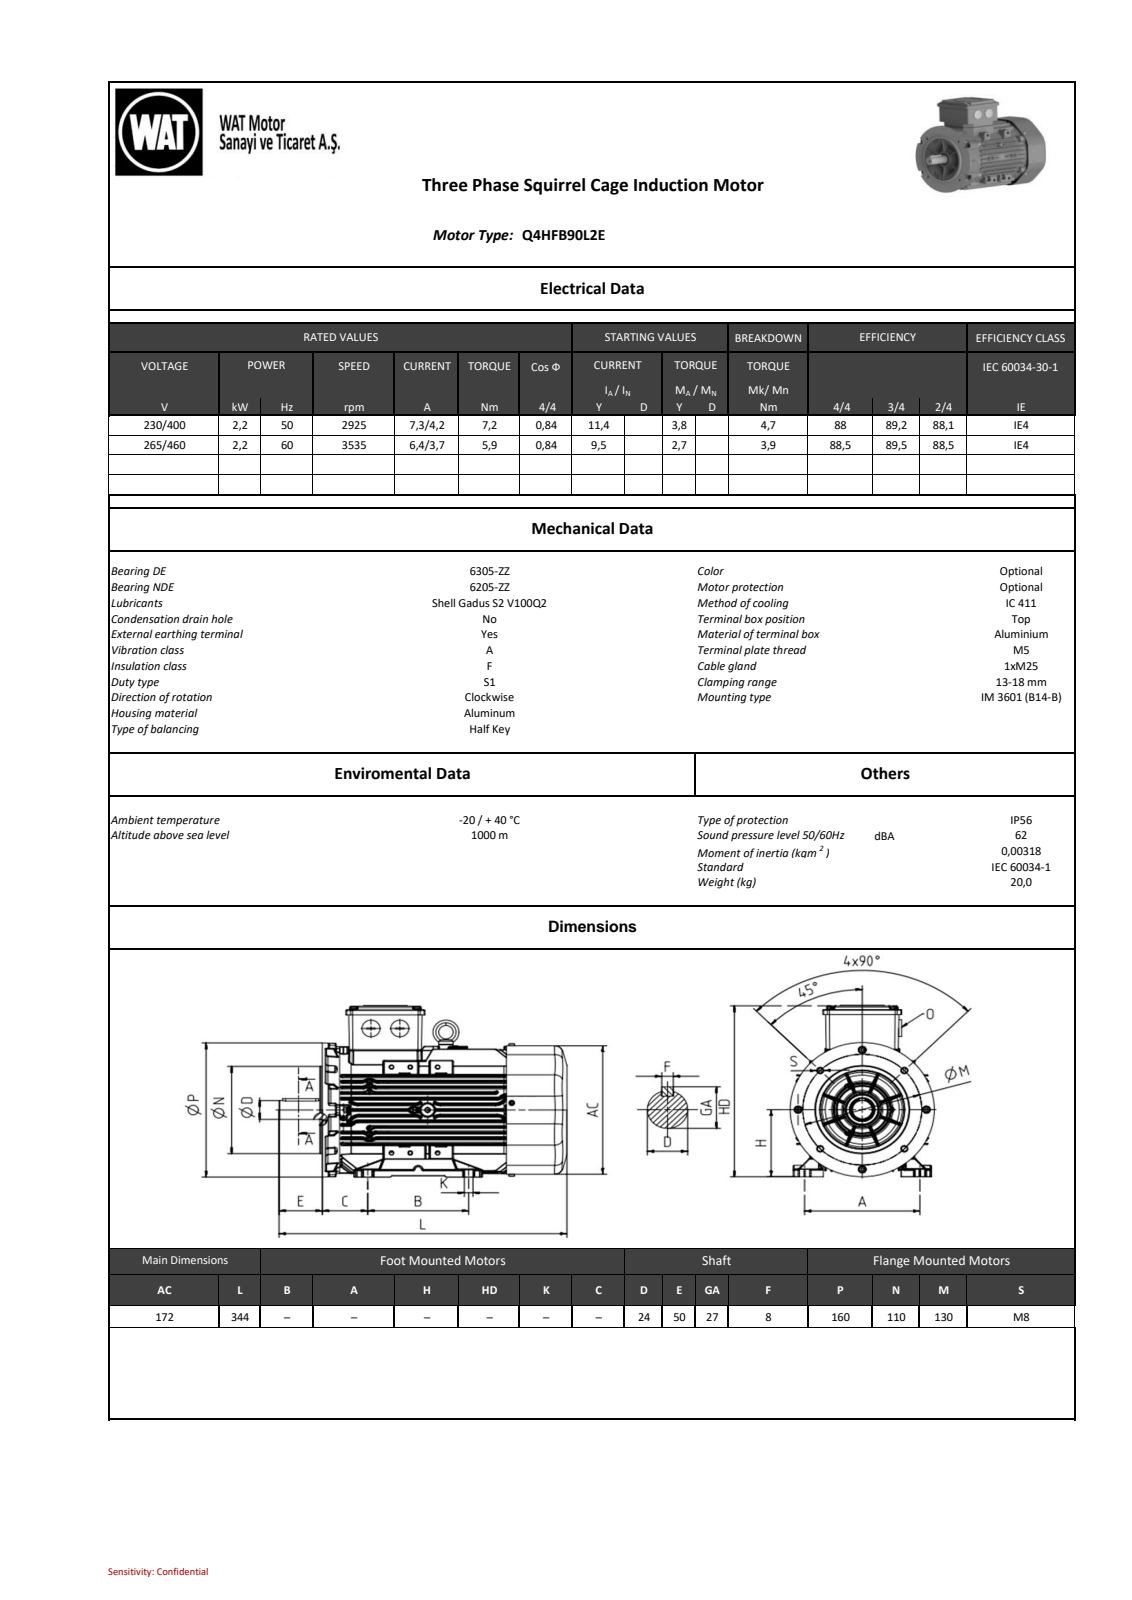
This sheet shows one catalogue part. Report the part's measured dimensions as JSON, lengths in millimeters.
{"part_name": "model1", "step_written_by": "SIEMENS PLM Software NX2206.8101 (AUTOMOTIVE_DESIGN)", "units": "millimeters", "bodies": {"solids": 0, "faces": 5192, "planar": 1321, "cylindrical": 2241, "other": 1630}, "overall_size": [343.54, 219.57, 178.35], "round_holes": [[6.8, 4], [9.87, 1], [37.42, 1], [79.79, 1], [97.79, 1], [115.78, 1]], "round_bosses_or_shafts": [[5, 8], [8, 7], [10, 5], [25, 3], [110, 1], [102.19, 1], [84.19, 1], [39.5, 1]], "partial_cylinders_radius": [[1, 629], [0.8, 527], [0.5, 143], [2, 96], [8, 28], [4, 10], [0.7, 7], [5.68, 7]], "face_to_face_distances": [7.5, 91.91, 8.93, 82.98, 23.57, 50.35, 7.37, 9.06, 90.35, 75.04], "hole_center_spacings": [91.93, 64.98, 65.03, 64.94, 65, 65.02, 65.06, 130]}
